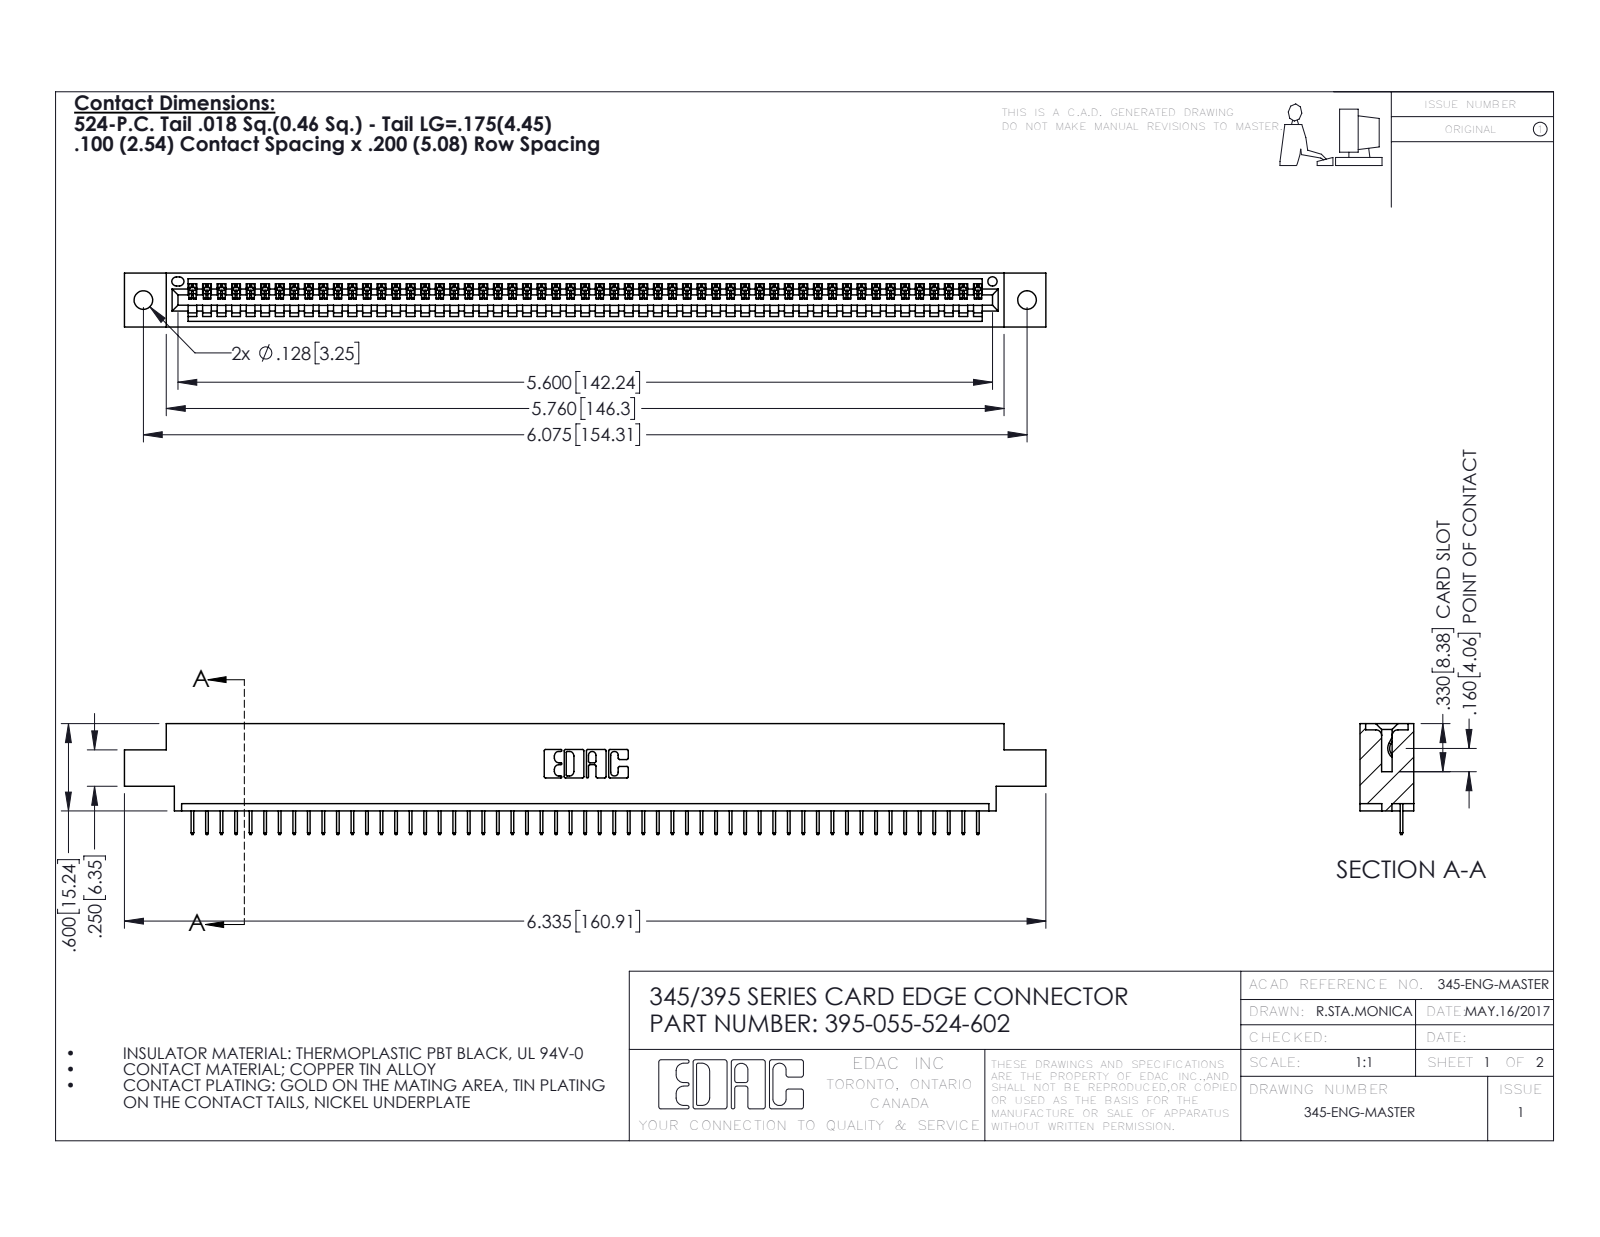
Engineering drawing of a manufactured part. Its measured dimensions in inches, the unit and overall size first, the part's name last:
Units: inches
Overall size (bounding box): 6.335 × 0.762 × 0.37
Round holes (diameter × count): ⌀0.128 ×2, ⌀0.064 ×1
Partial cylindrical surfaces — rounded edges, fillets, slot ends (radius × count): R0.006 ×110, R0.01 ×22, R0.007 ×6, R0.031 ×6, R0.026 ×3, R0.031 ×2, R0.04 ×2, R0.014 ×1
Main face-to-face distances: 0.072, 0.298, 0.37, 0.2, 0.098, 0.272, 0.025, 0.225, 0.072, 0.175
Hole centre spacings: 0.27, 5.839, 6.075
Volume: 0.917 in³ · Surface area: 29.92 in²
Bodies: 56 solids, 3540 faces (2614 planar, 926 cylindrical, 0 other)
Part name (STEP PRODUCT): 345-292-001_345-293-124; 345 Part_0.170 Offset - 0.128 Dia; 395-055-524-602
STEP written by: SolidWorks 2016 (CONFIG_CONTROL_DESIGN)
